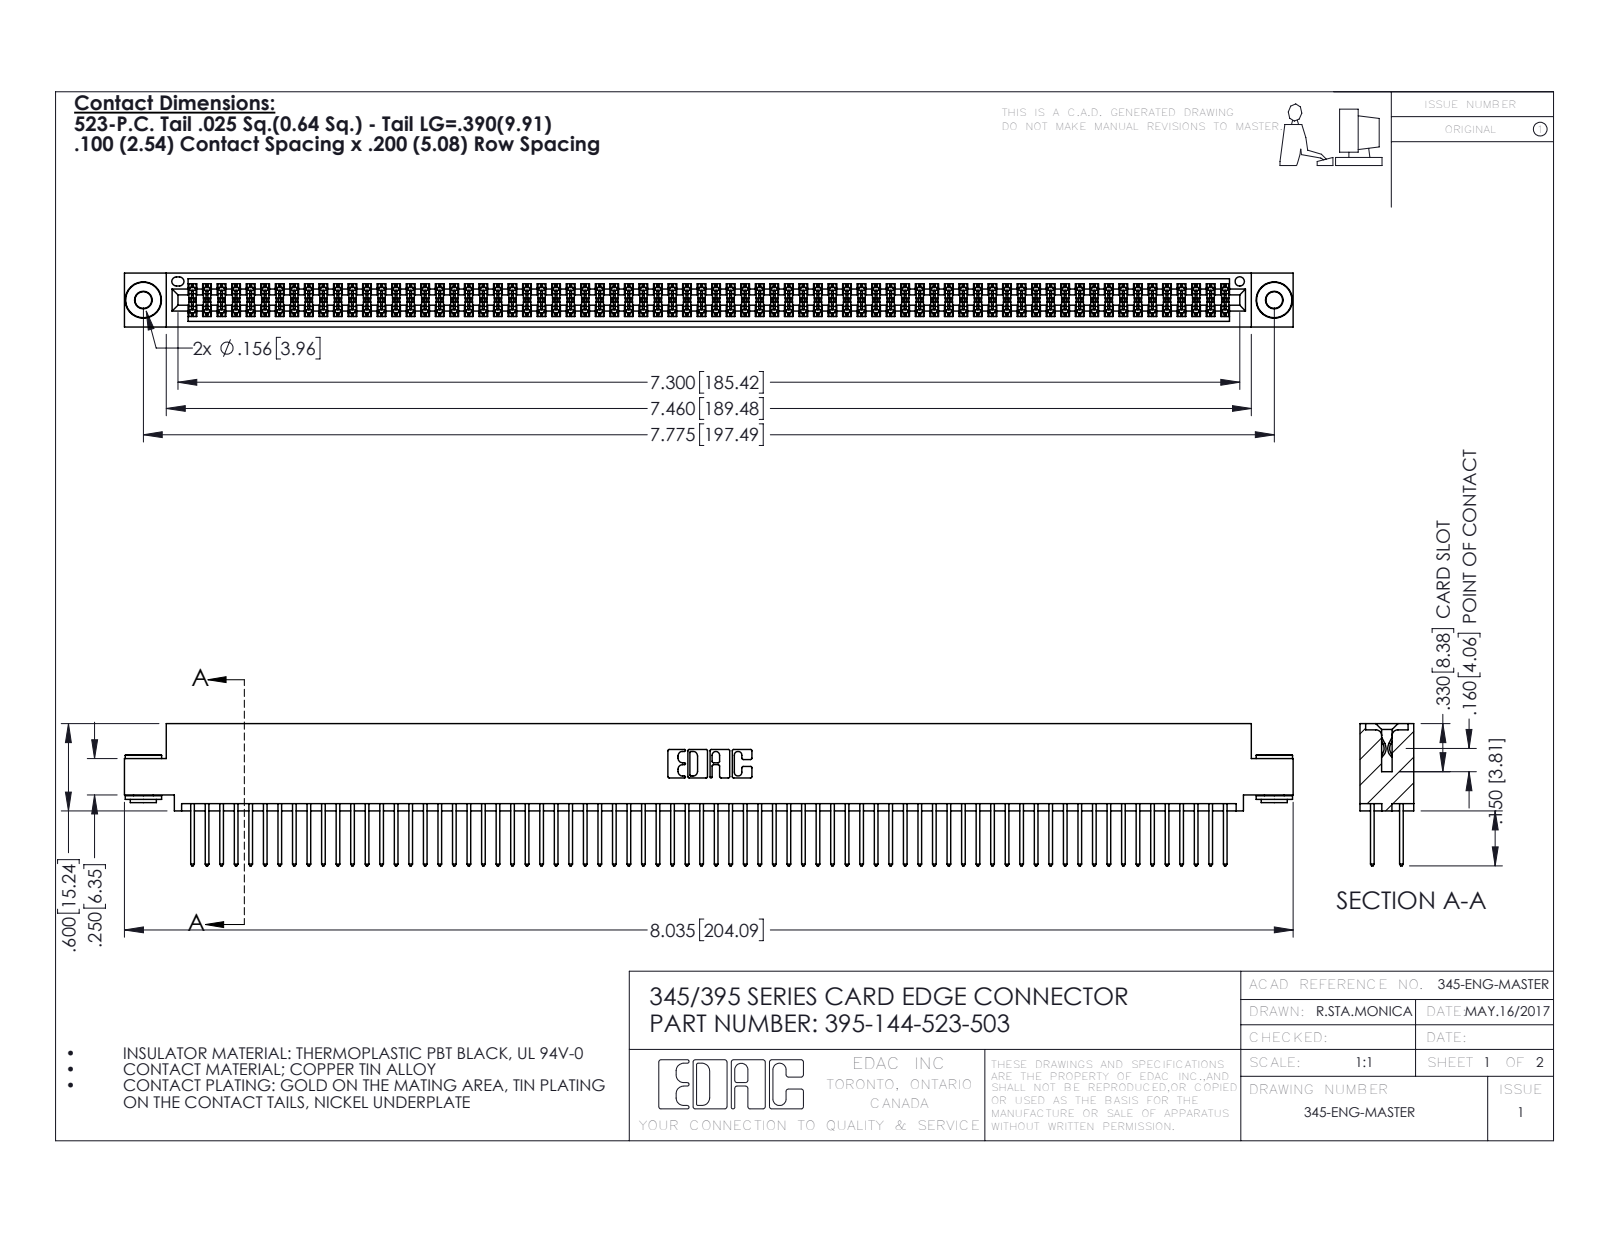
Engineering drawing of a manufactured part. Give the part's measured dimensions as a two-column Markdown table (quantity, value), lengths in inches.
| quantity | value |
| --- | --- |
| part name | 395-144-523-503; 345-292-001_345-293-123; 345 Part_0.110 Offset - 0.156 Dia-TH; 345-250-002_345-250-002-102 |
| STEP written by | SolidWorks 2016 (CONFIG_CONTROL_DESIGN) |
| units | inches |
| bodies | 147 solids, 7368 faces (4846 planar, 2514 cylindrical, 8 other) |
| overall size | 8.035 × 0.977 × 0.37 |
| volume | 1.242 in³ |
| surface area | 50.03 in² |
| round holes (diameter × count) | 0.116 × 2, 0.156 × 2, 0.064 × 1 |
| round bosses / shafts (diameter × count) | 0.25 × 2, 0.18 × 2, 0.136 × 2 |
| partial cylindrical surfaces (radius × count) | 0.006 × 216, 0.01 × 144, 0.01 × 22, 0.007 × 6, 0.031 × 6, 0.026 × 3, 0.014 × 2, 0.019 × 2 |
| main face-to-face distances | 0.072, 0.298, 0.2, 0.025, 0.098, 0.272, 0.37, 0.225, 0.175, 0.149 |
| hole center spacings | 0.27, 7.539, 7.775 |
